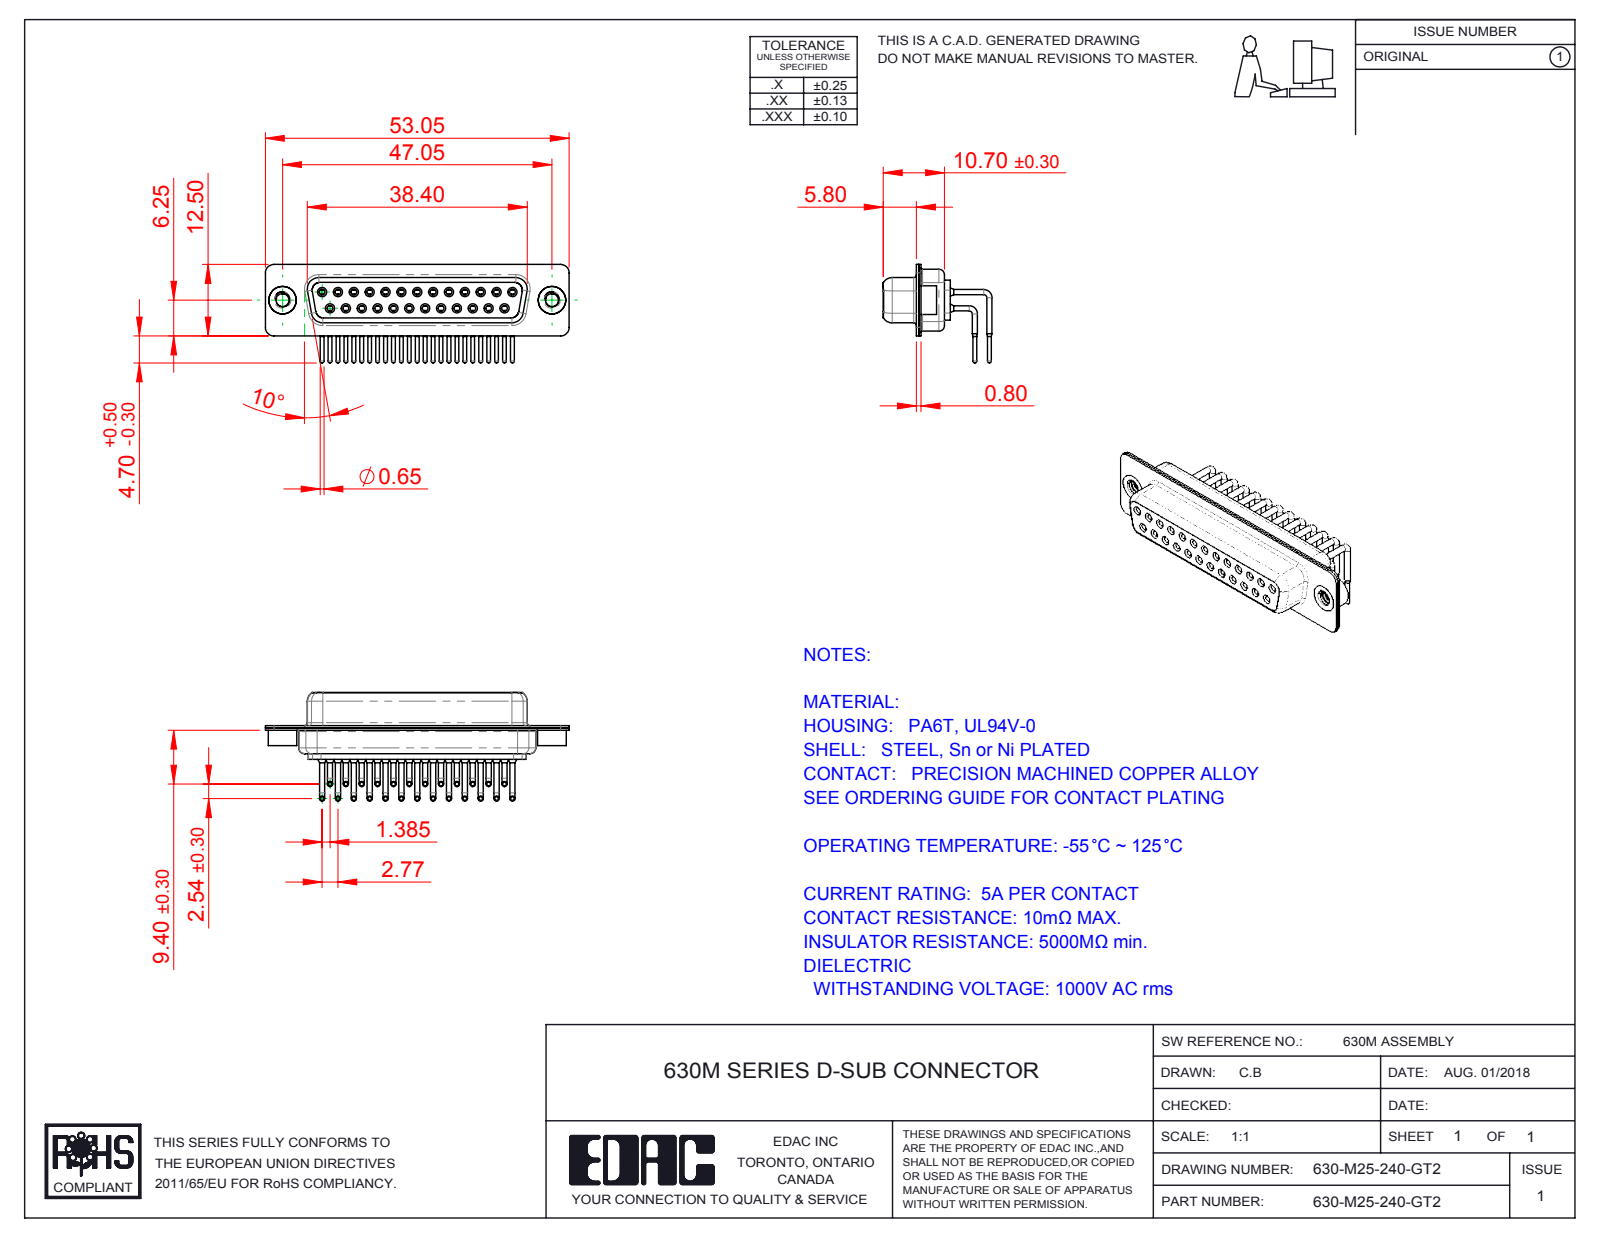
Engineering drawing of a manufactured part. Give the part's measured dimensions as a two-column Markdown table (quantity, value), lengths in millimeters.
| quantity | value |
| --- | --- |
| part name | 630M 4-40 Threaded Rivet; 630M Contact Row 1; 630M Shell Rear_25 Contacts; 630-M25-240-GT2 (+3 more) |
| STEP written by | SolidWorks 2016 (CONFIG_CONTROL_DESIGN) |
| units | millimeters |
| bodies | 30 solids, 1604 faces (442 planar, 712 cylindrical, 450 other) |
| overall size | 53.05 × 18.99 × 17.2 |
| volume | 3 898 mm³ |
| surface area | 9 728 mm² |
| round holes (diameter × count) | 1 × 25, 1.1 × 25, 1.7 × 25, 1.8 × 25, 2 × 25, 2.26 × 2, 4 × 2, 4.8 × 2 |
| round bosses / shafts (diameter × count) | 0.9 × 50, 1.6 × 25, 1.5 × 25, 0.65 × 25, 5 × 2, 4.9 × 2 |
| partial cylindrical surfaces (radius × count) | 1.5 × 16, 2 × 12, 1.35 × 10, 1.6 × 8, 0.25 × 4, 0.5 × 4, 0.6 × 4, 0.65 × 4 |
| main face-to-face distances | 0.4, 1.45, 8.95, 6.2, 2.3, 1.9, 8.5, 7.05, 0.45, 0.85 |
| hole center spacings | 3.16, 2.77, 5.54, 8.31, 11.08, 13.85, 5.04, 7.49 |
